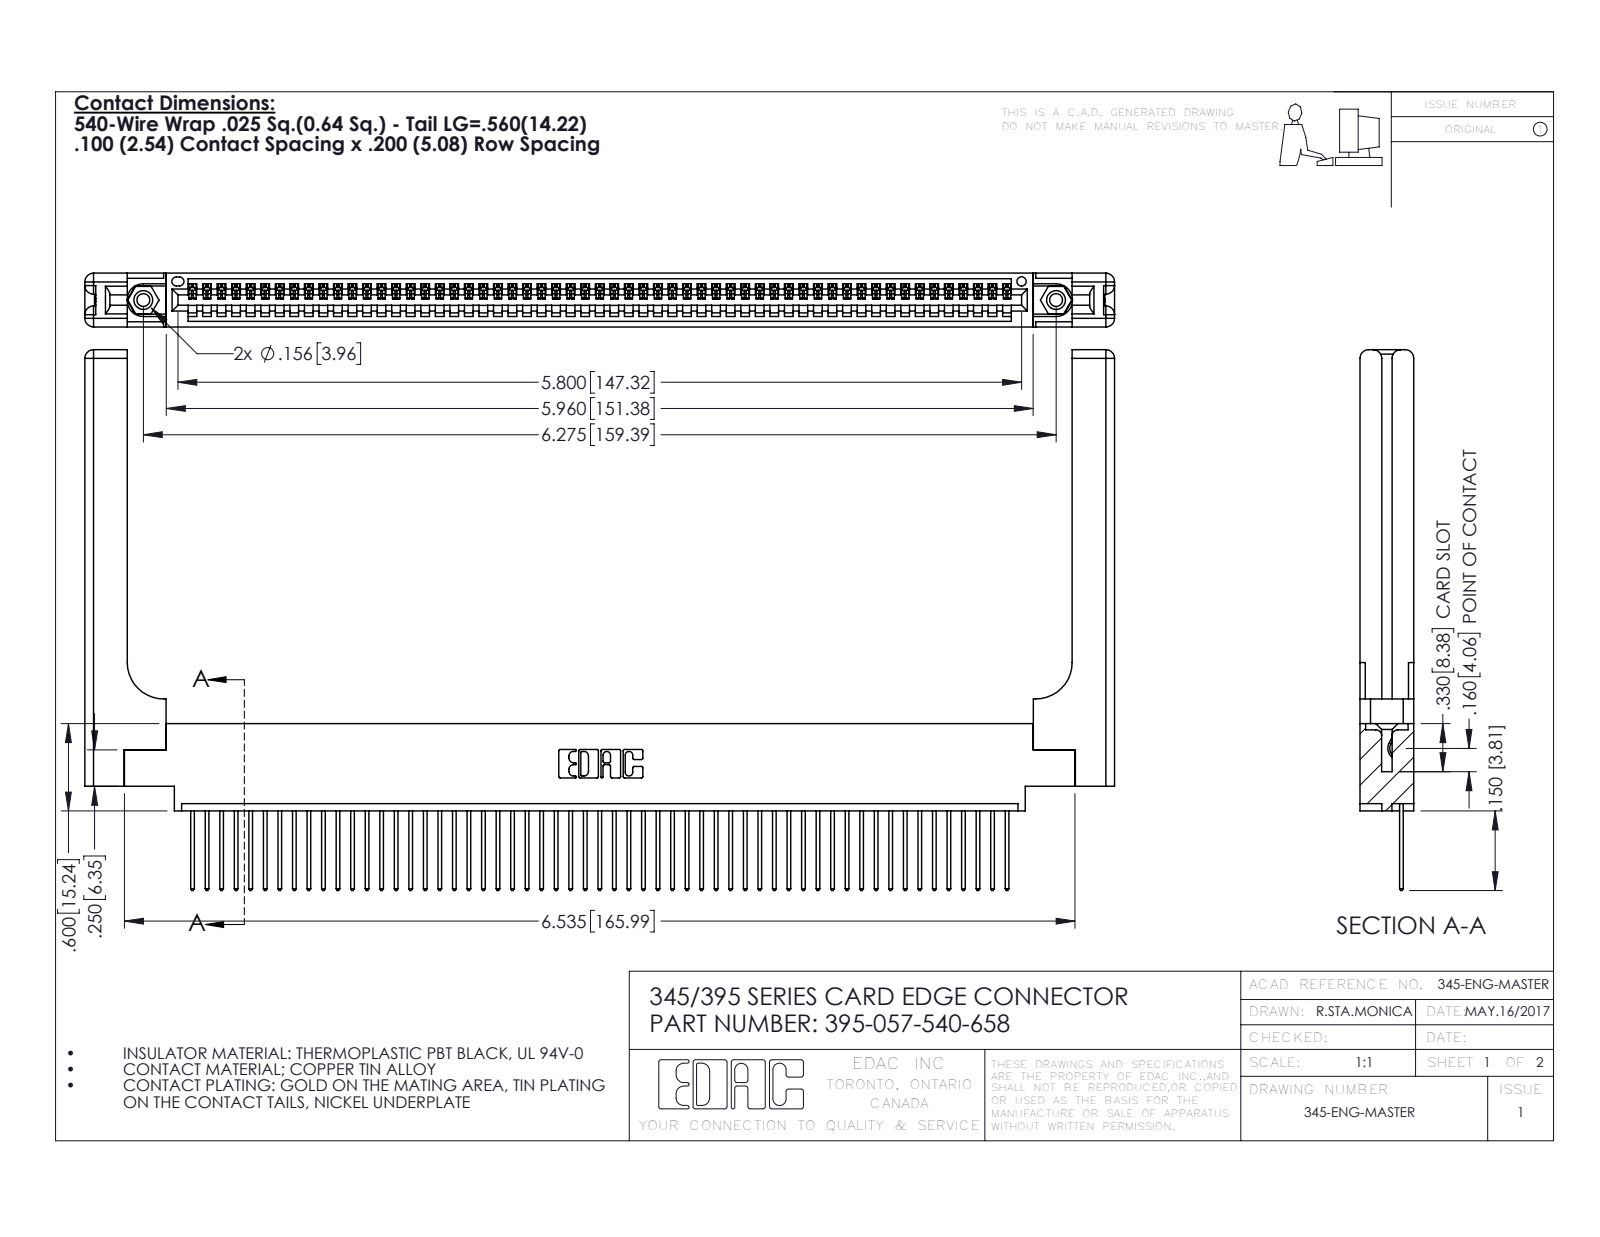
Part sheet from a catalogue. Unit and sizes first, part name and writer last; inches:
Units: inches
Overall size (bounding box): 7.079 × 3.717 × 0.37
Round holes (diameter × count): ⌀0.089 ×2, ⌀0.125 ×2, ⌀0.156 ×2, ⌀0.064 ×1
Round bosses / shafts (diameter × count): ⌀0.155 ×2
Partial cylindrical surfaces — rounded edges, fillets, slot ends (radius × count): R0.006 ×114, R0.01 ×114, R0.01 ×22, R0.06 ×16, R0.007 ×6, R0.031 ×6, R0.026 ×3, R0.03 ×2
Main face-to-face distances: 0.072, 0.37, 0.298, 0.098, 0.272, 0.025, 0.2, 0.225, 0.148, 0.15
Hole centre spacings: 0.27, 6.039, 6.275
Volume: 1.566 in³ · Surface area: 44.95 in²
Bodies: 62 solids, 3692 faces (2512 planar, 1120 cylindrical, 60 other)
Part name (STEP PRODUCT): 345-292-001_345-293-140; 345 Part_0.170 Offset - 0.156 Dia-TH; 345-220-058_345-220-058; 345-250-001_345-250-001-102 (+1 more)
STEP written by: SolidWorks 2016 (CONFIG_CONTROL_DESIGN)
